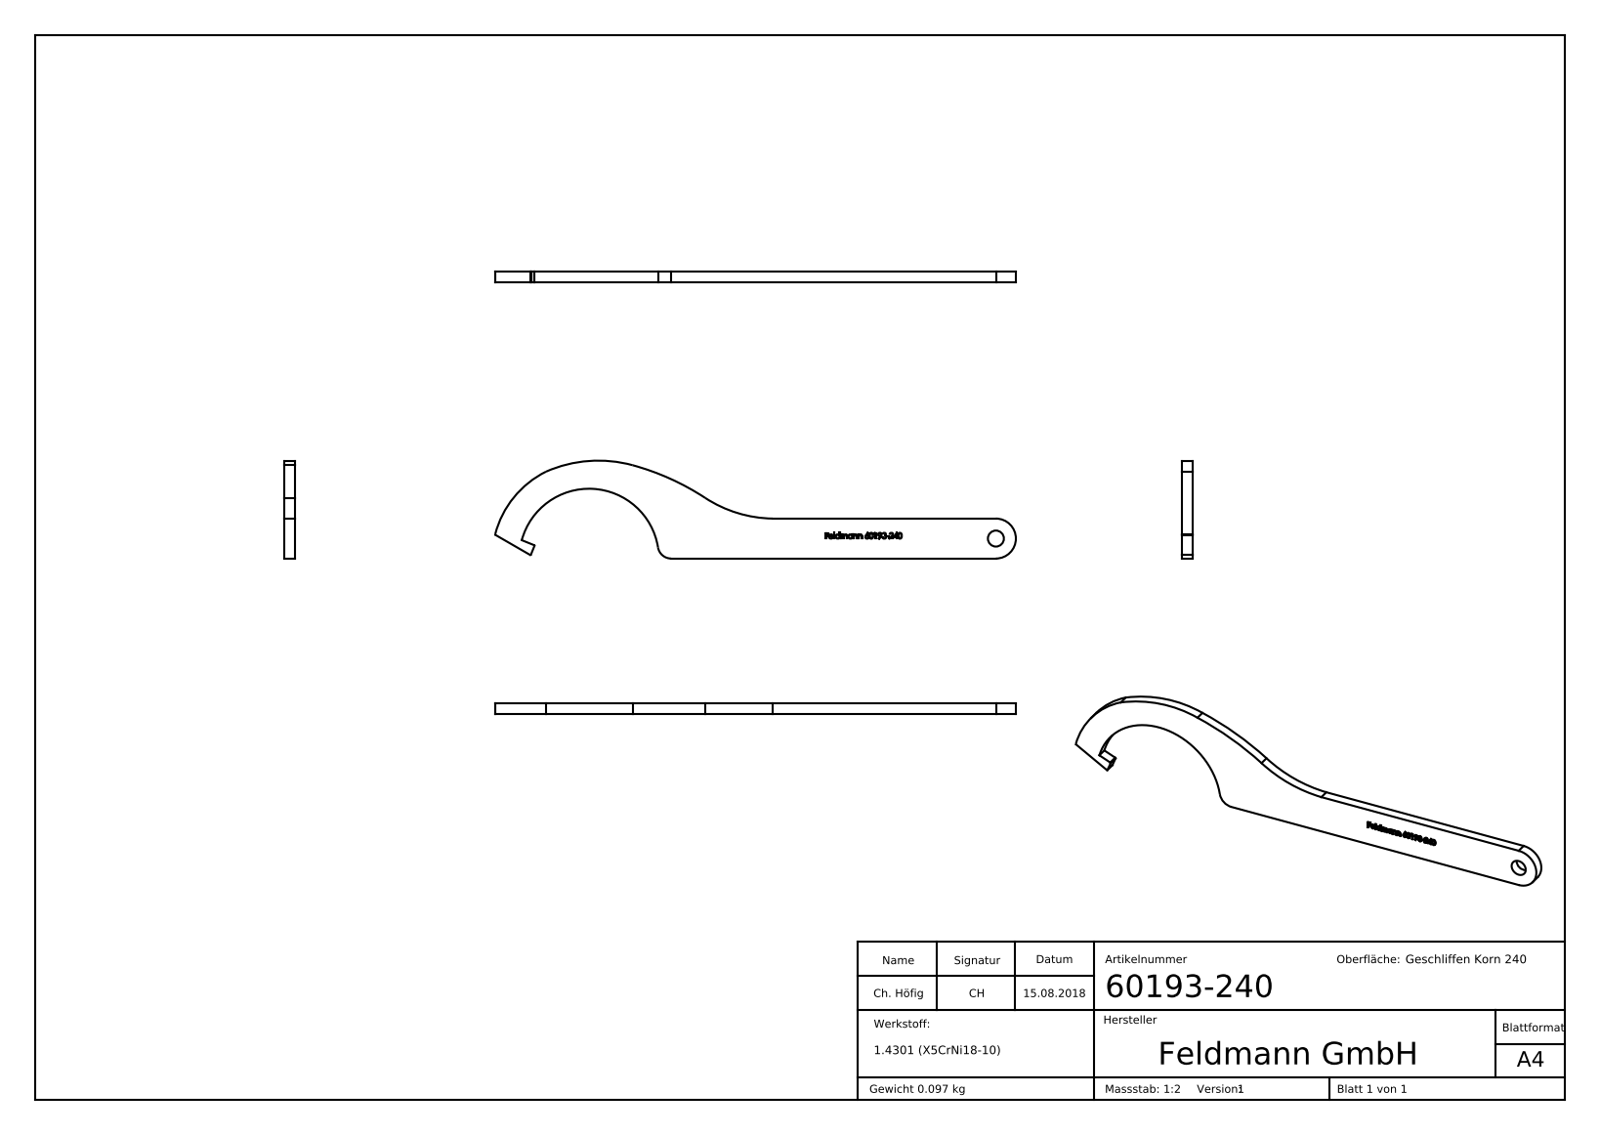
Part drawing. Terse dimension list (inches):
name: 60193-240
written by: SolidWorks 2015 (CONFIG_CONTROL_DESIGN)
unit: in
bodies: 1 solid, 241 faces (124 planar, 13 cylindrical, 104 other)
size: 7.695 × 1.447 × 0.157
volume: 0.751 in³; area: 12.49 in²
holes: 1× ⌀0.236
rounds: 3× R0.01, 1× R0.197, 1× R0.295, 1× R1.031, 1× R1.433, 1× R1.873, 1× R1.924, 1× R3.759
face distances: 0.157, 0.591, 0.154, 0.295, 0.187, 0.017, 0.079, 0.104, 0.612, 0.127
